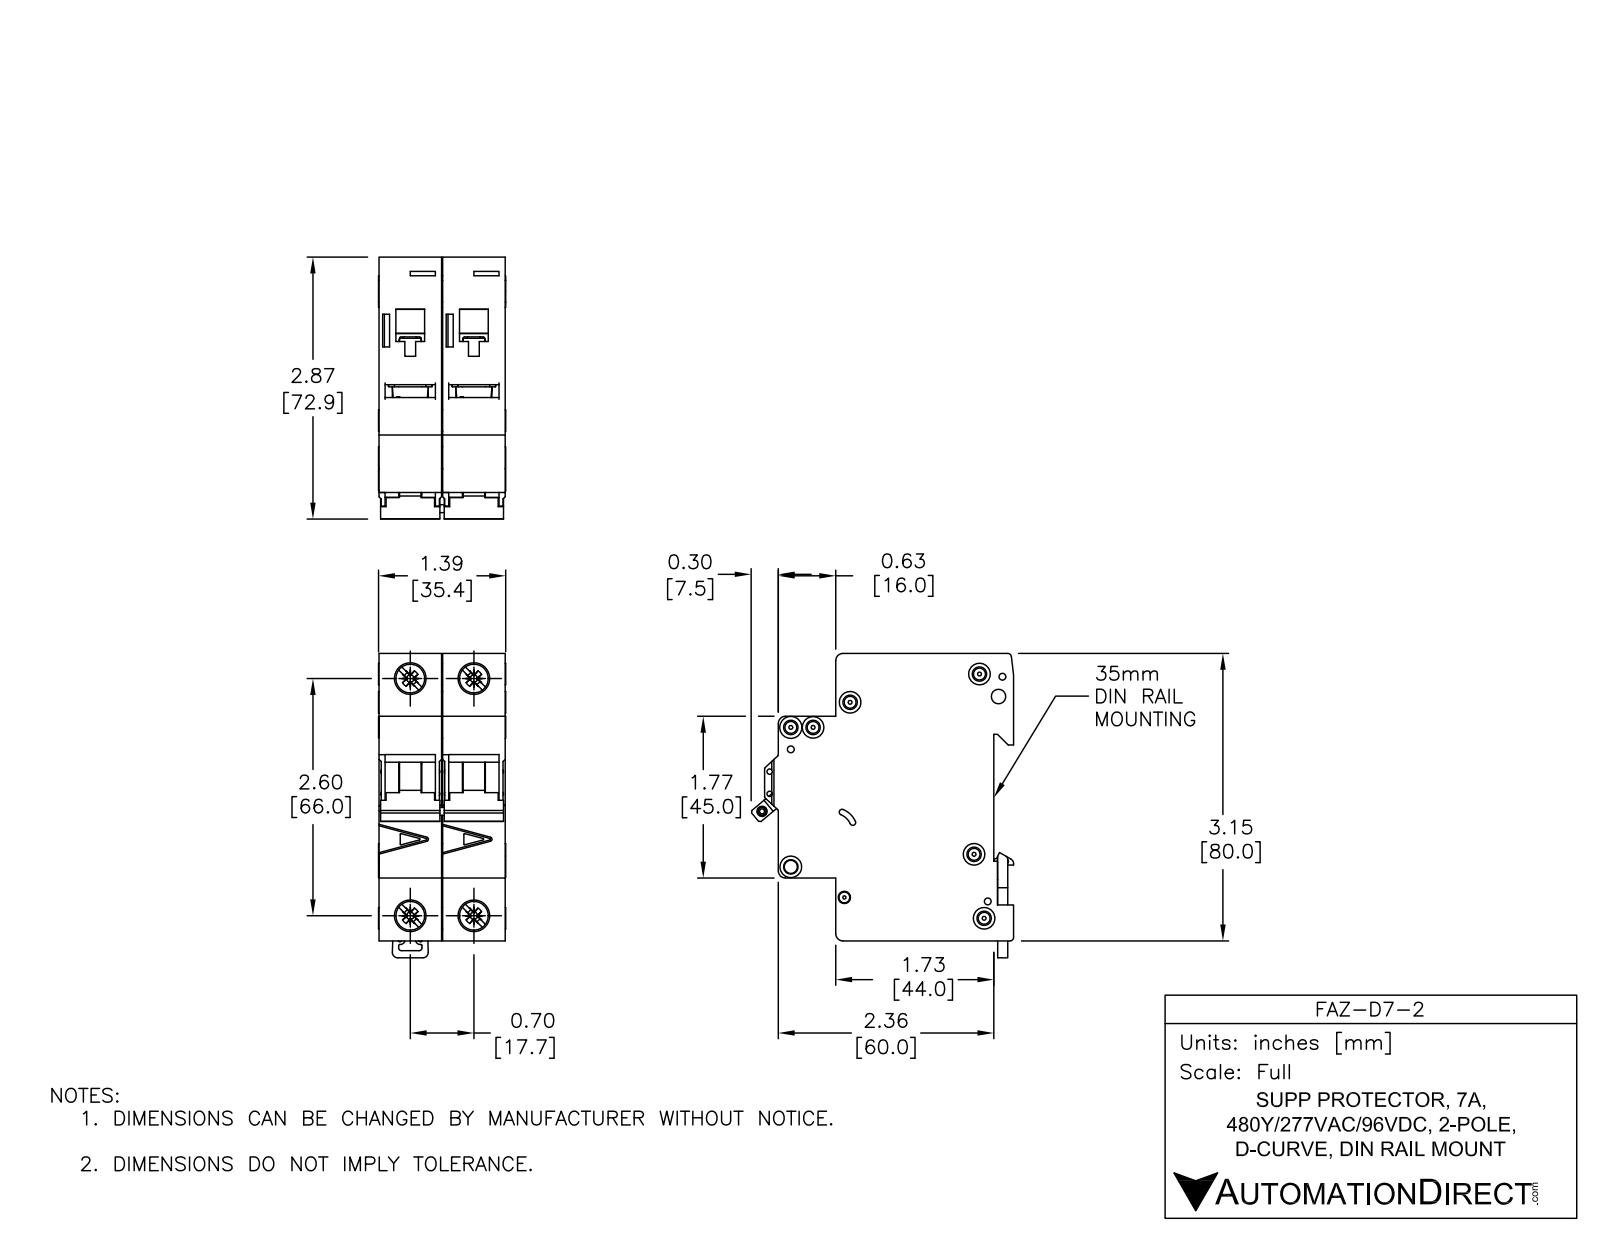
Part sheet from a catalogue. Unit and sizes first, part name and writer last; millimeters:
Units: millimetres
Overall size (bounding box): 84.78 × 73.04 × 35.4
Round holes (diameter × count): ⌀3.6 ×6, ⌀1.9 ×3, ⌀1.09 ×2, ⌀1.5 ×2, ⌀4 ×2, ⌀7.15 ×2, ⌀8.2 ×2, ⌀2.15 ×1, ⌀2.2 ×1, ⌀2.55 ×1, ⌀3.3 ×1, ⌀3.4 ×1
Round bosses / shafts (diameter × count): ⌀6 ×4, ⌀8.2 ×2, ⌀2.5 ×2
Partial cylindrical surfaces — rounded edges, fillets, slot ends (radius × count): R0.25 ×49, R0.5 ×19, R2 ×10, R0.2 ×8, R1 ×8, R0.8 ×2, R1.8 ×2, R3 ×2
Main face-to-face distances: 17.7, 17.5, 35.2, 79.48, 5.5, 49.5, 44, 65.5, 60, 16
Hole centre spacings: 6.2, 13.64, 17.7, 66, 68.33, 4.81, 5.19, 5.61
Volume: 149 808 mm³ · Surface area: 38 799 mm²
Bodies: 8 solids, 1104 faces (466 planar, 396 cylindrical, 242 other)
Part name (STEP PRODUCT): FAZ-D7-2
STEP written by: SolidWorks 2014 (AUTOMOTIVE_DESIGN)
